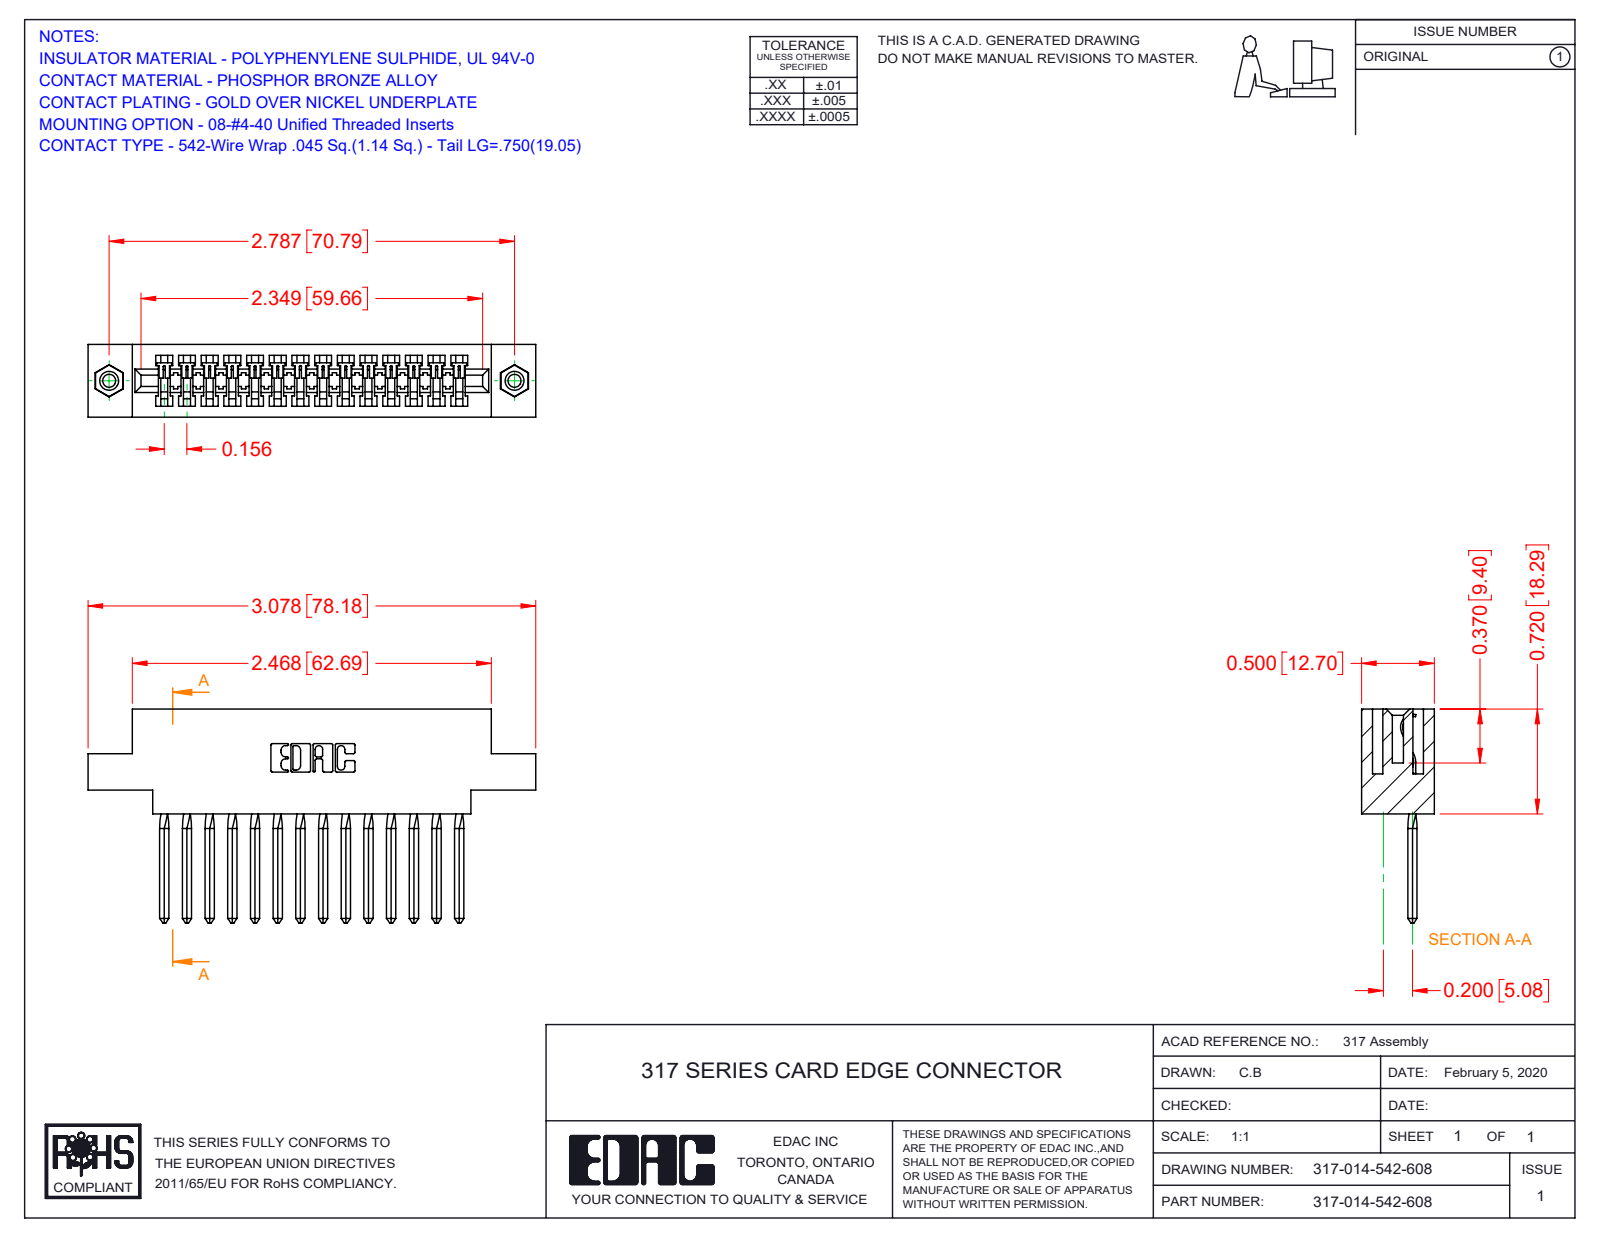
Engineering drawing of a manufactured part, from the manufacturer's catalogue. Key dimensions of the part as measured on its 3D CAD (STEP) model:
Part name (STEP PRODUCT): 345-250-001_345-250-003-102; 317-290-003_542; 317-014-542-608; 317 Part_.156 Dia - TI
STEP written by: SolidWorks 2016 (CONFIG_CONTROL_DESIGN)
Units: inches
Bodies: 17 solids, 1212 faces (986 planar, 154 cylindrical, 72 other)
Overall size (bounding box): 3.078 × 1.47 × 0.5
Volume: 0.691 in³ · Surface area: 20.48 in²
Round holes (diameter × count): ⌀0.089 ×2, ⌀0.125 ×2, ⌀0.156 ×2
Round bosses / shafts (diameter × count): ⌀0.155 ×2
Partial cylindrical surfaces — rounded edges, fillets, slot ends (radius × count): R0.006 ×28, R0.01 ×22, R0.007 ×6, R0.031 ×6, R0.026 ×3, R0.074 ×1, R0.089 ×1, R0.1 ×1
Main face-to-face distances: 0.5, 0.075, 0.425, 0.11, 0.35, 0.065, 0.22, 0.136, 0.72, 0.116
Hole centre spacings: 2.787
